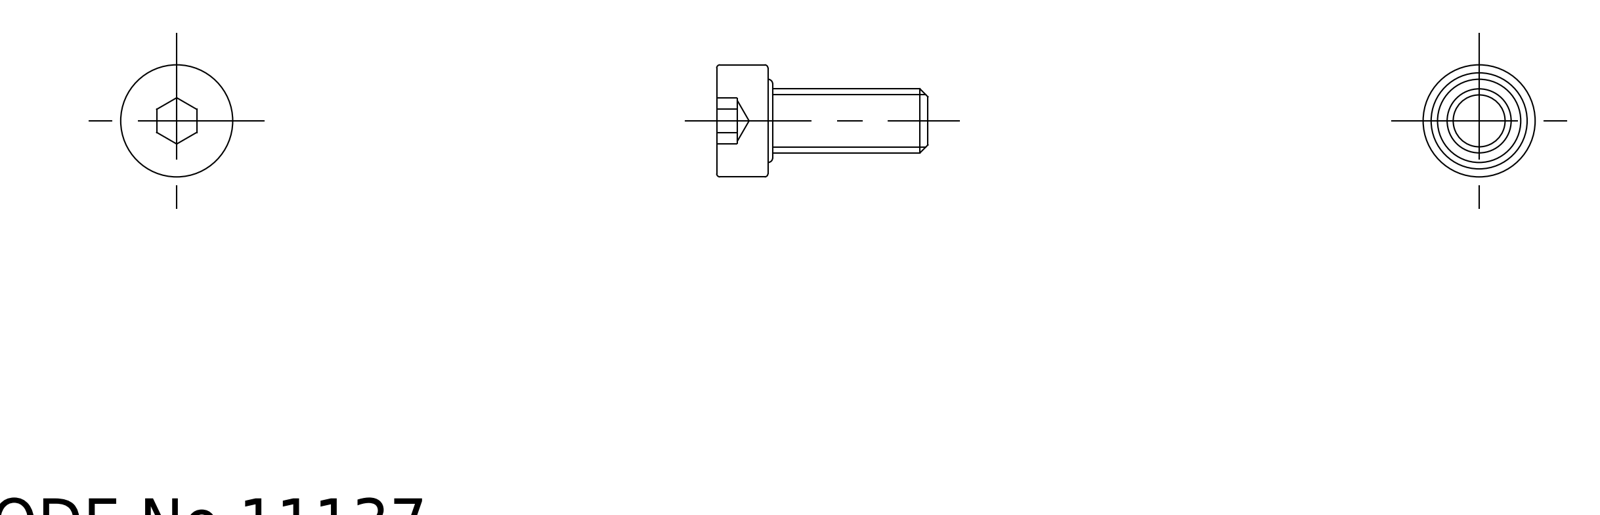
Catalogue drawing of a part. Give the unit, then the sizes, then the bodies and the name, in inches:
Units: inches
Overall size (bounding box): 0.52 × 0.276 × 0.276
Round holes (diameter × count): ⌀0.236 ×1
Round bosses / shafts (diameter × count): ⌀0.276 ×1, ⌀0.157 ×1
Main face-to-face distances: 0.114, 0.52, 0.406, 0.126, 0.394, 0.098, 0.051, 0.063, 0.075, 0.469
Volume: 0.015 in³ · Surface area: 0.485 in²
Bodies: 2 solids, 27 faces (11 planar, 6 cylindrical, 10 other)
Part name (STEP PRODUCT): screw; TL_418_M4_10
STEP written by: SolidWorks 2015 (AUTOMOTIVE_DESIGN)
